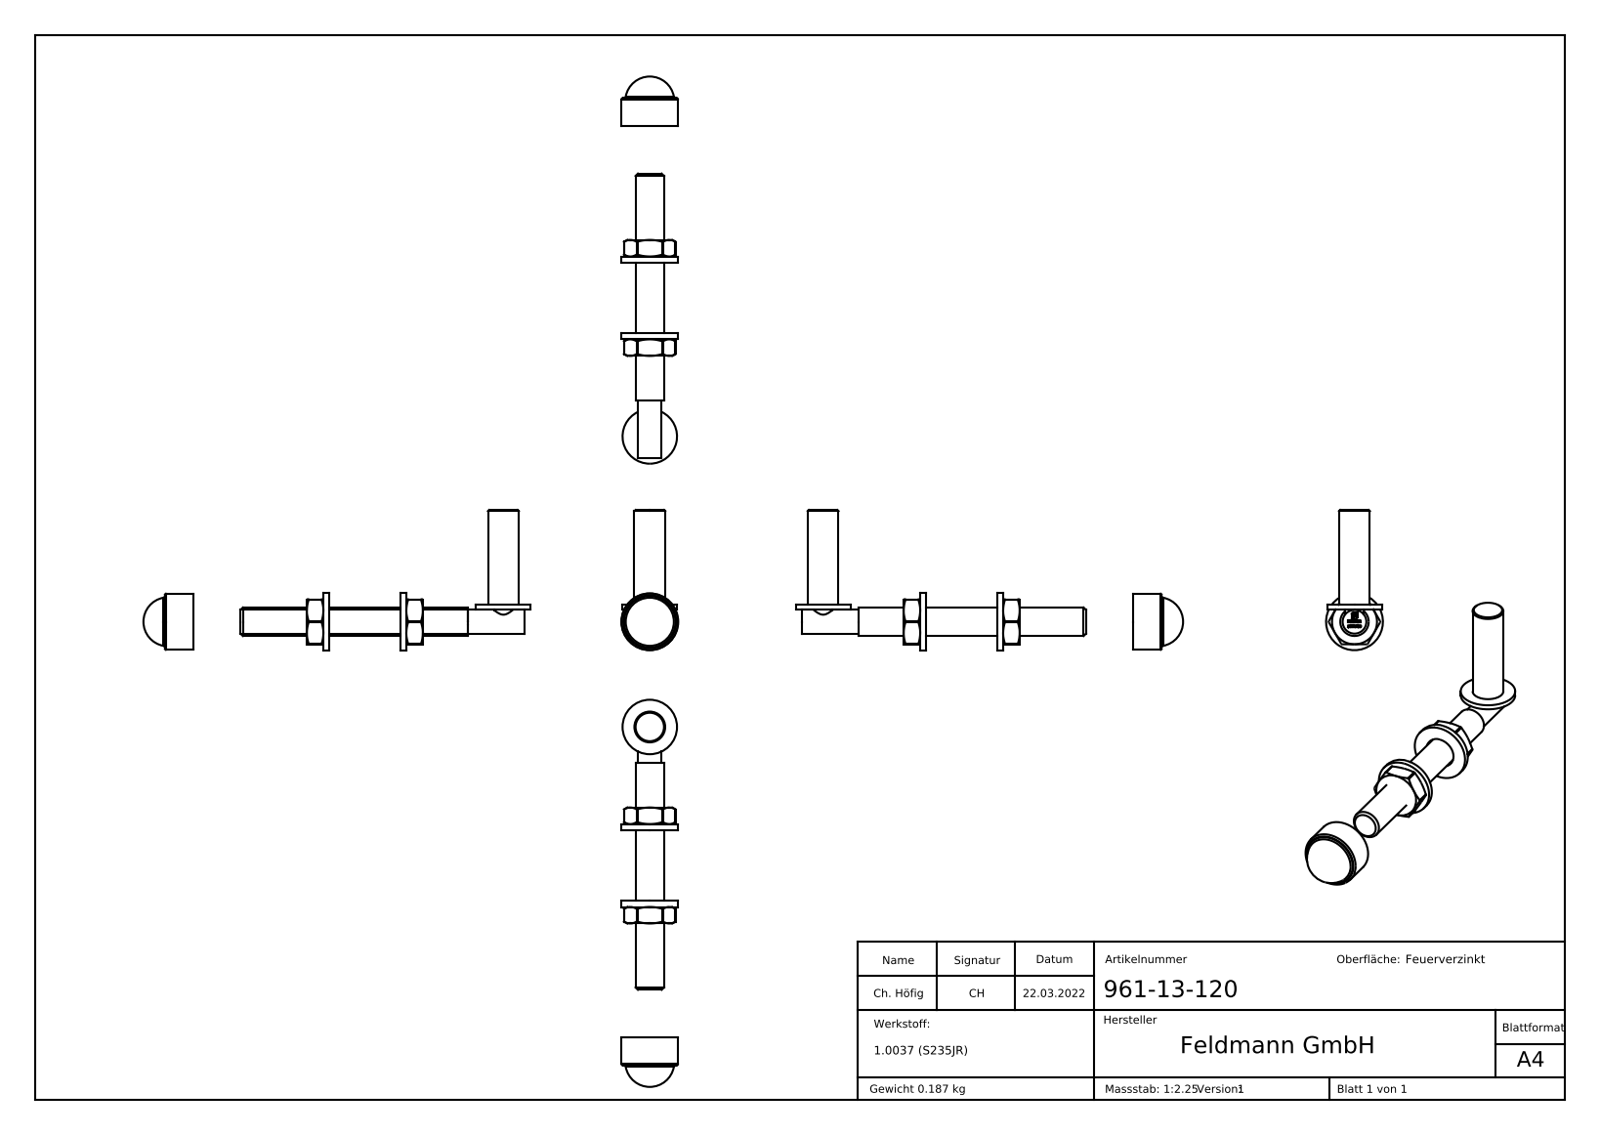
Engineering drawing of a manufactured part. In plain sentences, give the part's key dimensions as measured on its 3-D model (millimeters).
The part is named "961-13-120; DIN 936 M8-M24_DIN 936 M12; DIN 125 M4-M20_DIN 125 M12; 961-1X-XXX Teil1_961-13-120 Teil1 (+1 more)". Its 3-D file was written by "SolidWorks 2018 (CONFIG_CONTROL_DESIGN)". It is 6 solids with 356 faces: 182 planar, 25 cylindrical and 149 other. Overall it measures 163.5 by 59.2 by 24 millimeters. Its volume is 25 711 cubic millimeters and its surface area 14 157 square millimeters. Round holes: 1 of diameter 10.2, 1 of diameter 13, 1 of diameter 19. Round bosses or shafts: 1 of diameter 24, 1 of diameter 23.8, 1 of diameter 23, 1 of diameter 13, 1 of diameter 12, 1 of diameter 10, 1 of diameter 8. Partial cylindrical surfaces (rounded edges, fillets, slot ends): 6 of radius 0.5. The main face-to-face distances are 19, 2.5, 32.5, 35, 42, 9.5, 7, 39.5, 30, 2.
